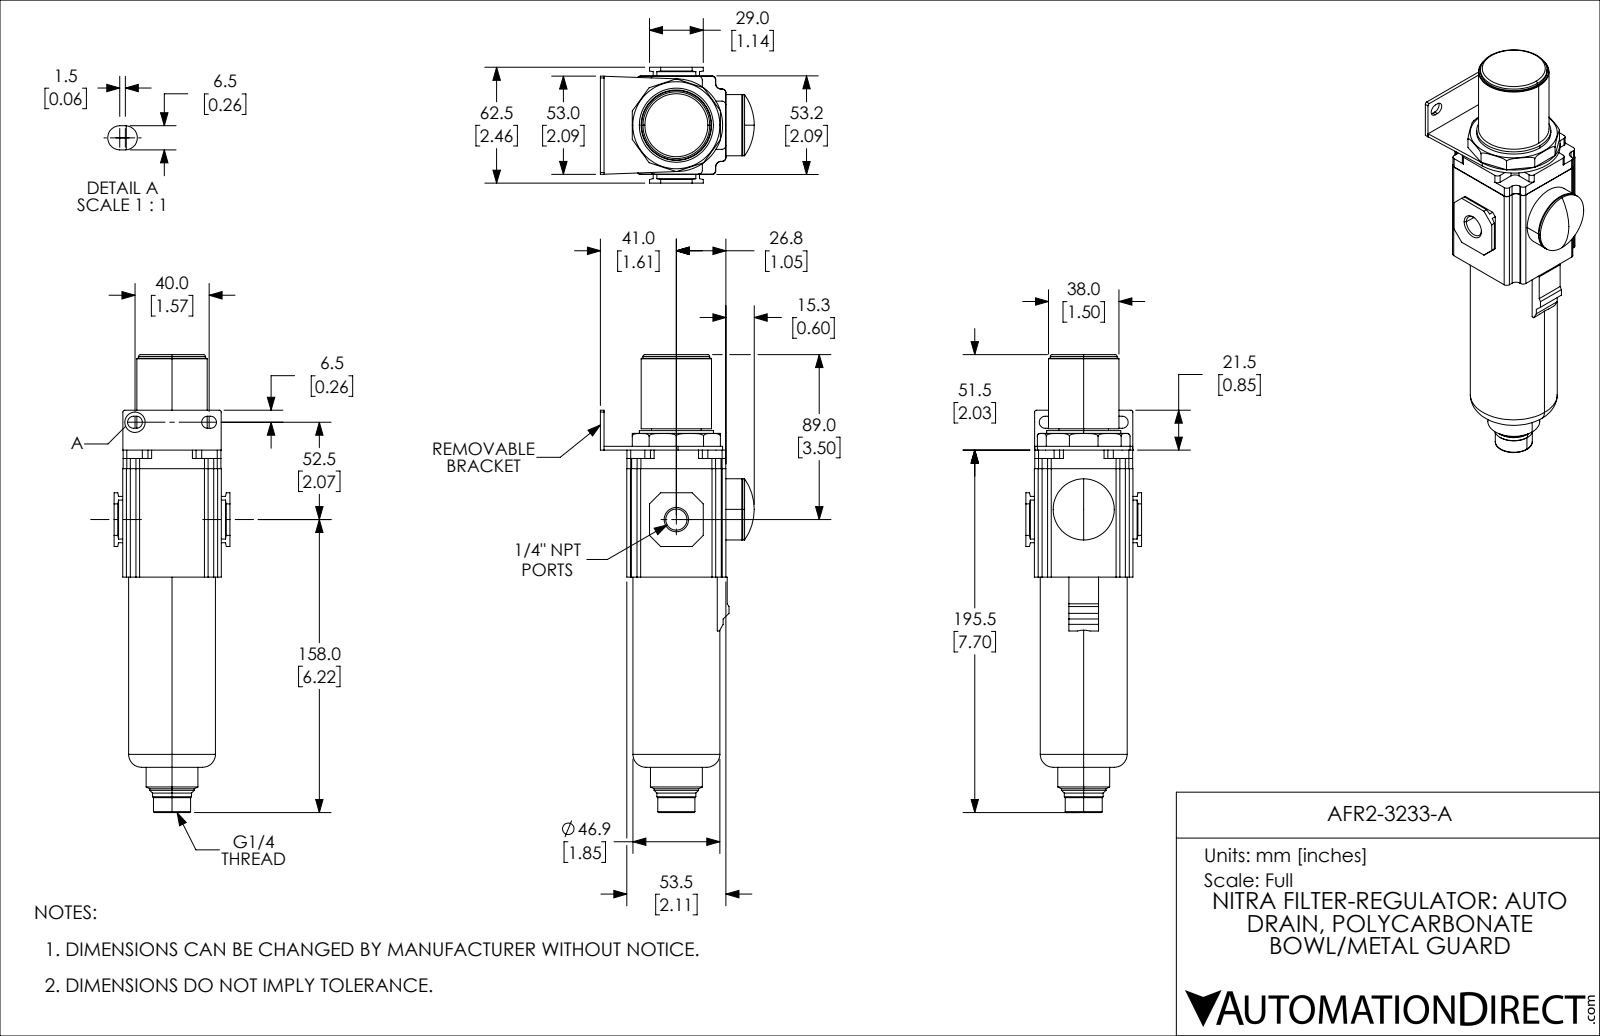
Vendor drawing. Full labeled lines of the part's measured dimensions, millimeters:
Part name (STEP PRODUCT): AFR2-3233-A
STEP written by: SolidWorks 2019 (CONFIG_CONTROL_DESIGN)
Units: millimetres
Bodies: 1 solid, 221 faces (124 planar, 71 cylindrical, 26 other)
Overall size (bounding box): 247 × 83.03 × 62.5
Volume: 452 721 mm³ · Surface area: 51 631 mm²
Round holes (diameter × count): ⌀11.45 ×2
Round bosses / shafts (diameter × count): ⌀46.9 ×1, ⌀40 ×1, ⌀38 ×1, ⌀36 ×1, ⌀33 ×1, ⌀28 ×1, ⌀26.78 ×1, ⌀24 ×1
Partial cylindrical surfaces — rounded edges, fillets, slot ends (radius × count): R2 ×24, R3 ×12, R3.25 ×4, R1 ×2, R25 ×1
Main face-to-face distances: 2, 53.2, 53.5, 4.65, 57.85, 14.25, 12.25, 67.75, 51.5, 49.5
